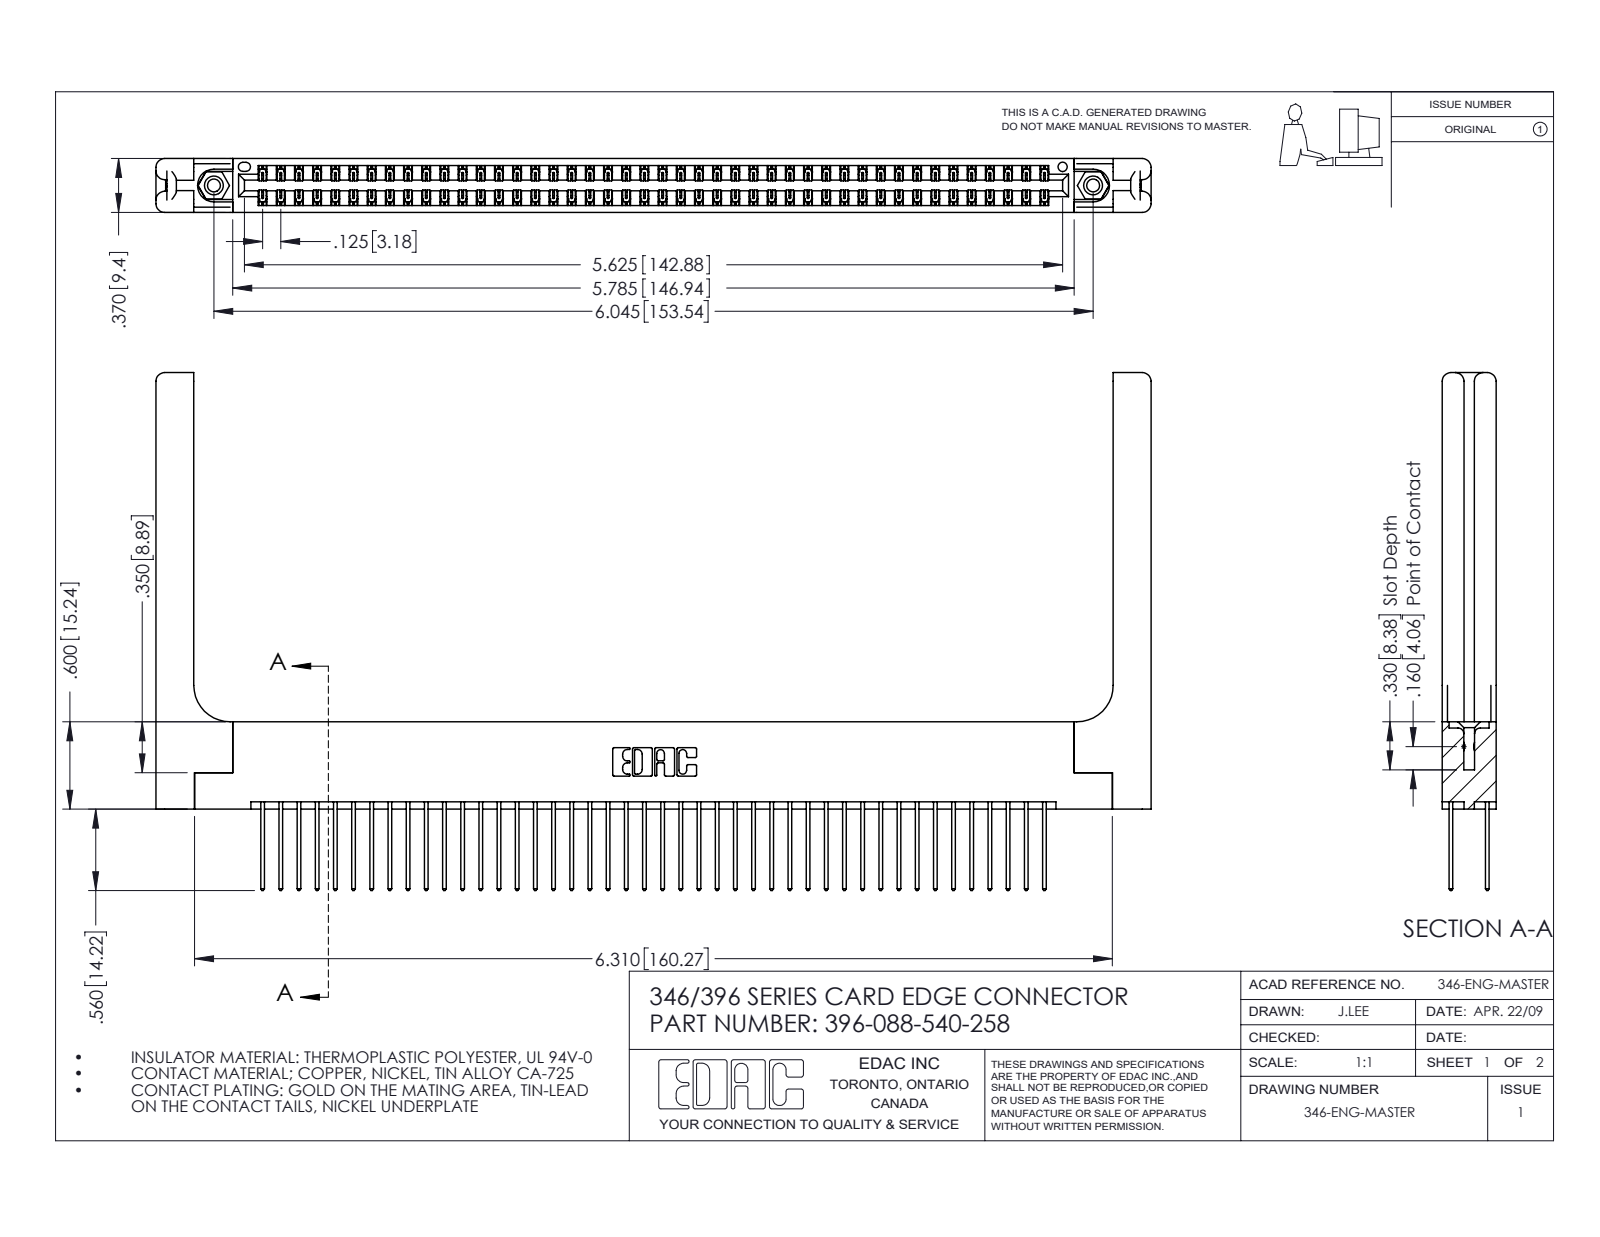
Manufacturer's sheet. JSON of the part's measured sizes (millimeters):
{"part_name": "345-250-001_345-250-001-102; 345-292-001_345-293-140; 396-088-540-258; 346 Part_Flush Mounting Lugs - 0.156 Dia-TH (+1 more)", "step_written_by": "SolidWorks 2016 (CONFIG_CONTROL_DESIGN)", "units": "millimeters", "bodies": {"solids": 93, "faces": 4954, "planar": 3304, "cylindrical": 1590, "other": 60}, "overall_size": [173.8, 90.4, 9.4], "volume_mm3": 24790, "surface_area_mm2": 30350, "round_holes": [[2.3, 2], [3.2, 2], [4, 2], [1.6, 1]], "round_bosses_or_shafts": [[3.9, 2]], "partial_cylinders_radius": [[0.2, 132], [0.3, 88], [0.3, 22], [1.5, 16], [0.2, 6], [0.8, 6], [0.7, 3], [0.4, 2]], "face_to_face_distances": [1.2, 8.2, 1.8, 9.4, 6.4, 0.6, 7.6, 3.8, 3.8, 7], "hole_center_spacings": [6.2, 148.2, 153.5]}
